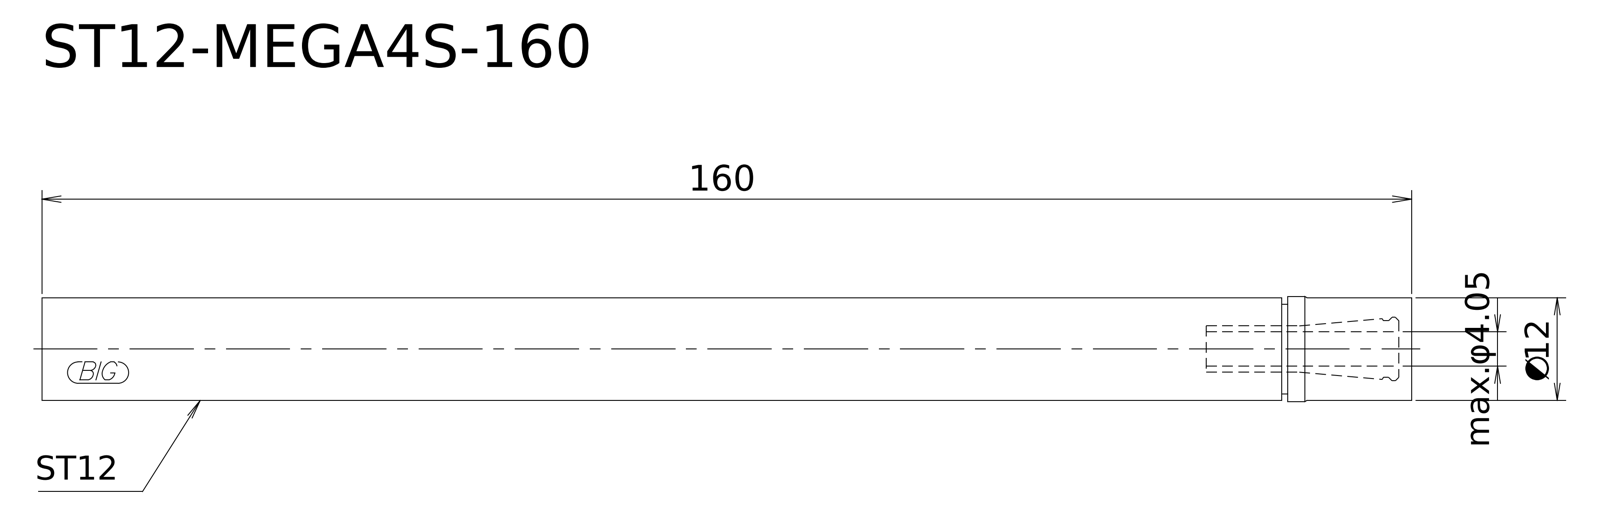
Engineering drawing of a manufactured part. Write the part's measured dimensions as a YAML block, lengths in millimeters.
step_written_by: "Kubotek KeyCreator V8.5.1 (14335) (CONFIG_CONTROL_DESIGN)"
units: millimeters
bodies: {solids: 1, faces: 9, planar: 3, cylindrical: 4, other: 2}
overall_size: [160, 12.3, 12.3]
volume: 18084
surface_area: 6305
round_bosses_or_shafts:
  - {diameter: 12.3, count: 1}
  - {diameter: 12, count: 1}
  - {diameter: 10.5, count: 1}
face_to_face_distances: [160, 14.5, 145.5]
